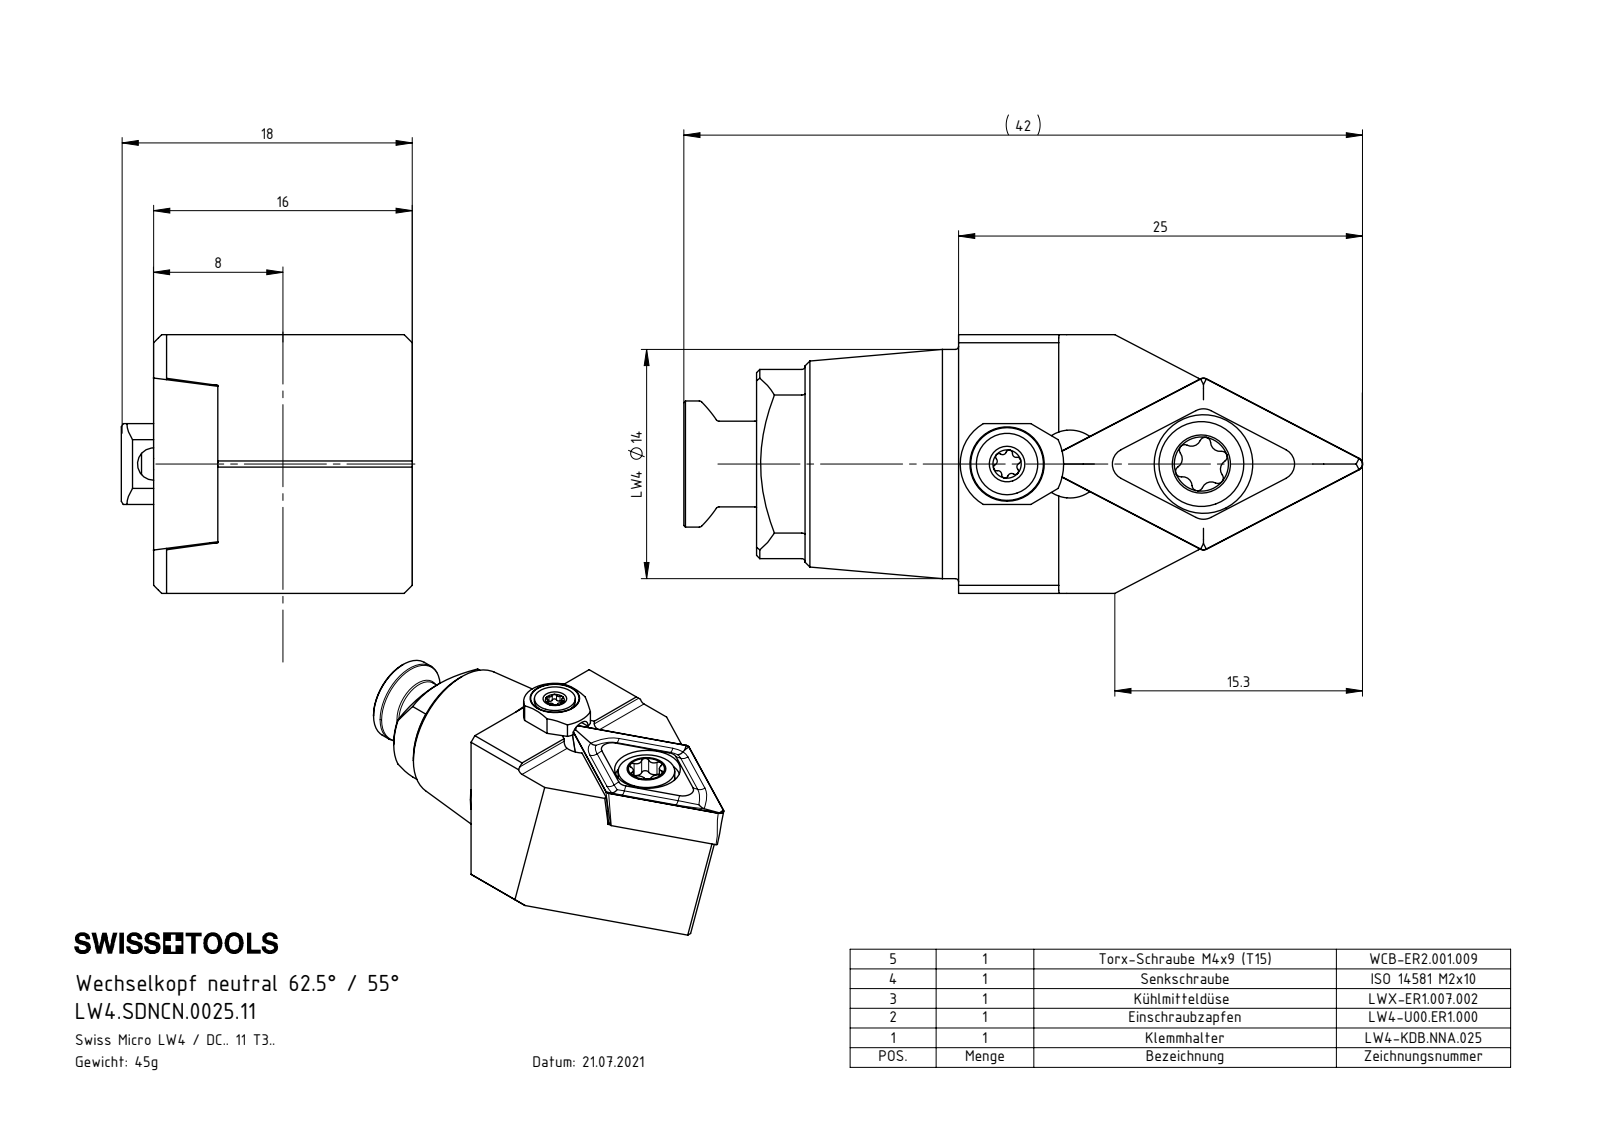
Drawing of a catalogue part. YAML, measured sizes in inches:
part_name: "DCMT11T304; LW4-KDB.NNA.025_A; LW4-U00.ER1.000_B; LWX-ER1.007.002 (+3 more)"
step_written_by: "SolidWorks 2022 (CONFIG_CONTROL_DESIGN)"
units: inches
bodies: {solids: 6, faces: 266, planar: 69, cylindrical: 82, other: 115}
overall_size: [1.654, 0.709, 0.63]
volume: 0.334
surface_area: 5.549
round_holes:
  - {diameter: 0.098, count: 2}
  - {diameter: 0.063, count: 1}
  - {diameter: 0.079, count: 1}
  - {diameter: 0.118, count: 1}
  - {diameter: 0.13, count: 1}
  - {diameter: 0.165, count: 1}
  - {diameter: 0.173, count: 1}
  - {diameter: 0.217, count: 1}
  - {diameter: 0.24, count: 1}
round_bosses_or_shafts:
  - {diameter: 0.558, count: 1}
  - {diameter: 0.303, count: 1}
  - {diameter: 0.236, count: 1}
  - {diameter: 0.209, count: 1}
  - {diameter: 0.207, count: 1}
  - {diameter: 0.197, count: 1}
  - {diameter: 0.157, count: 1}
  - {diameter: 0.15, count: 1}
partial_cylinders:
  - {radius: 0.008, count: 8}
  - {radius: 0.009, count: 6}
  - {radius: 0.013, count: 6}
  - {radius: 0.023, count: 6}
  - {radius: 0.02, count: 1}
  - {radius: 0.039, count: 1}
  - {radius: 0.114, count: 1}
  - {radius: 0.138, count: 1}
face_to_face_distances: [0.63, 0.474, 0.156, 0.598, 0.125, 0.031, 0.295, 0.118, 0.079, 0.492]
hole_center_spacings: [0.154, 0.32, 0.325, 0.473, 0.478]
